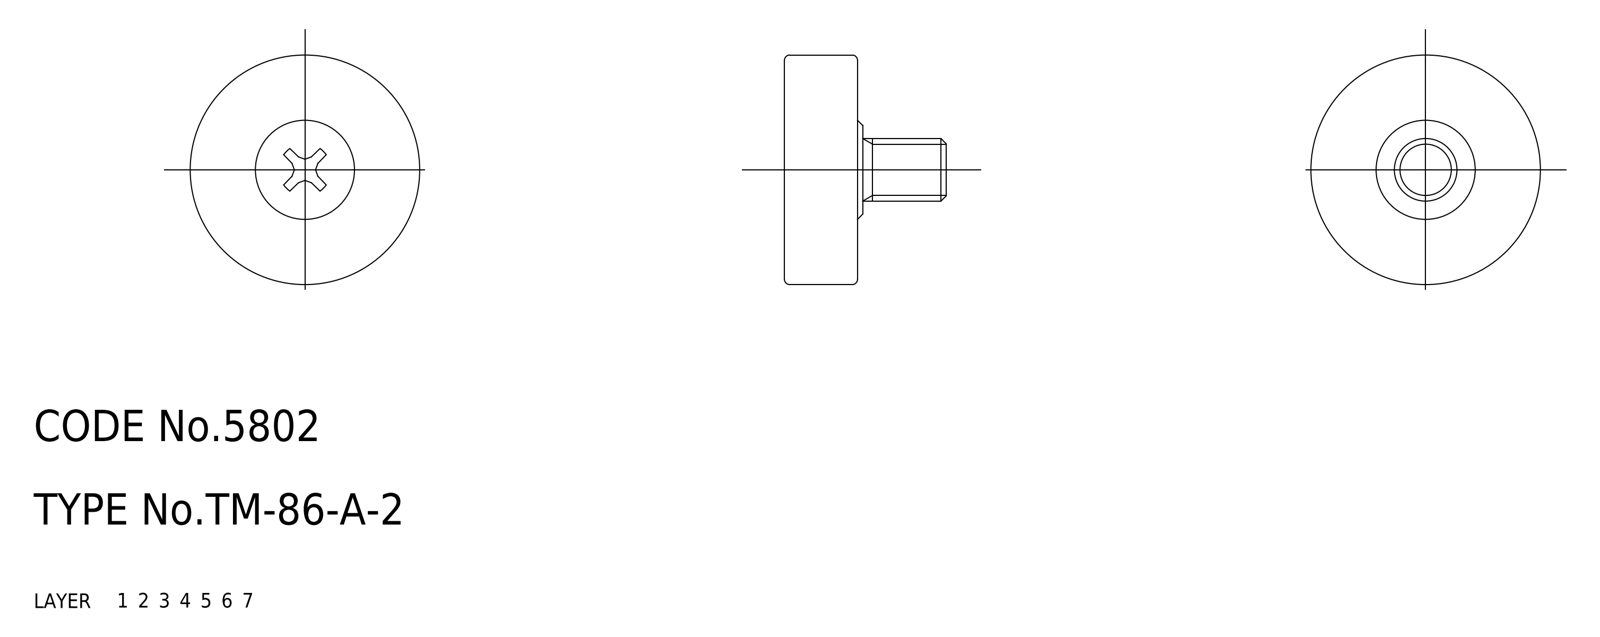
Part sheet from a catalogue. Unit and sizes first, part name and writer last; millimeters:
Units: millimetres
Overall size (bounding box): 22 × 22 × 15.5
Volume: 2 897 mm³ · Surface area: 1 902 mm²
Bodies: 1 solid, 49 faces (0 planar, 0 cylindrical, 49 other)
Part name (STEP PRODUCT): roller
STEP written by: CADfix (AUTOMOTIVE_DESIGN)
